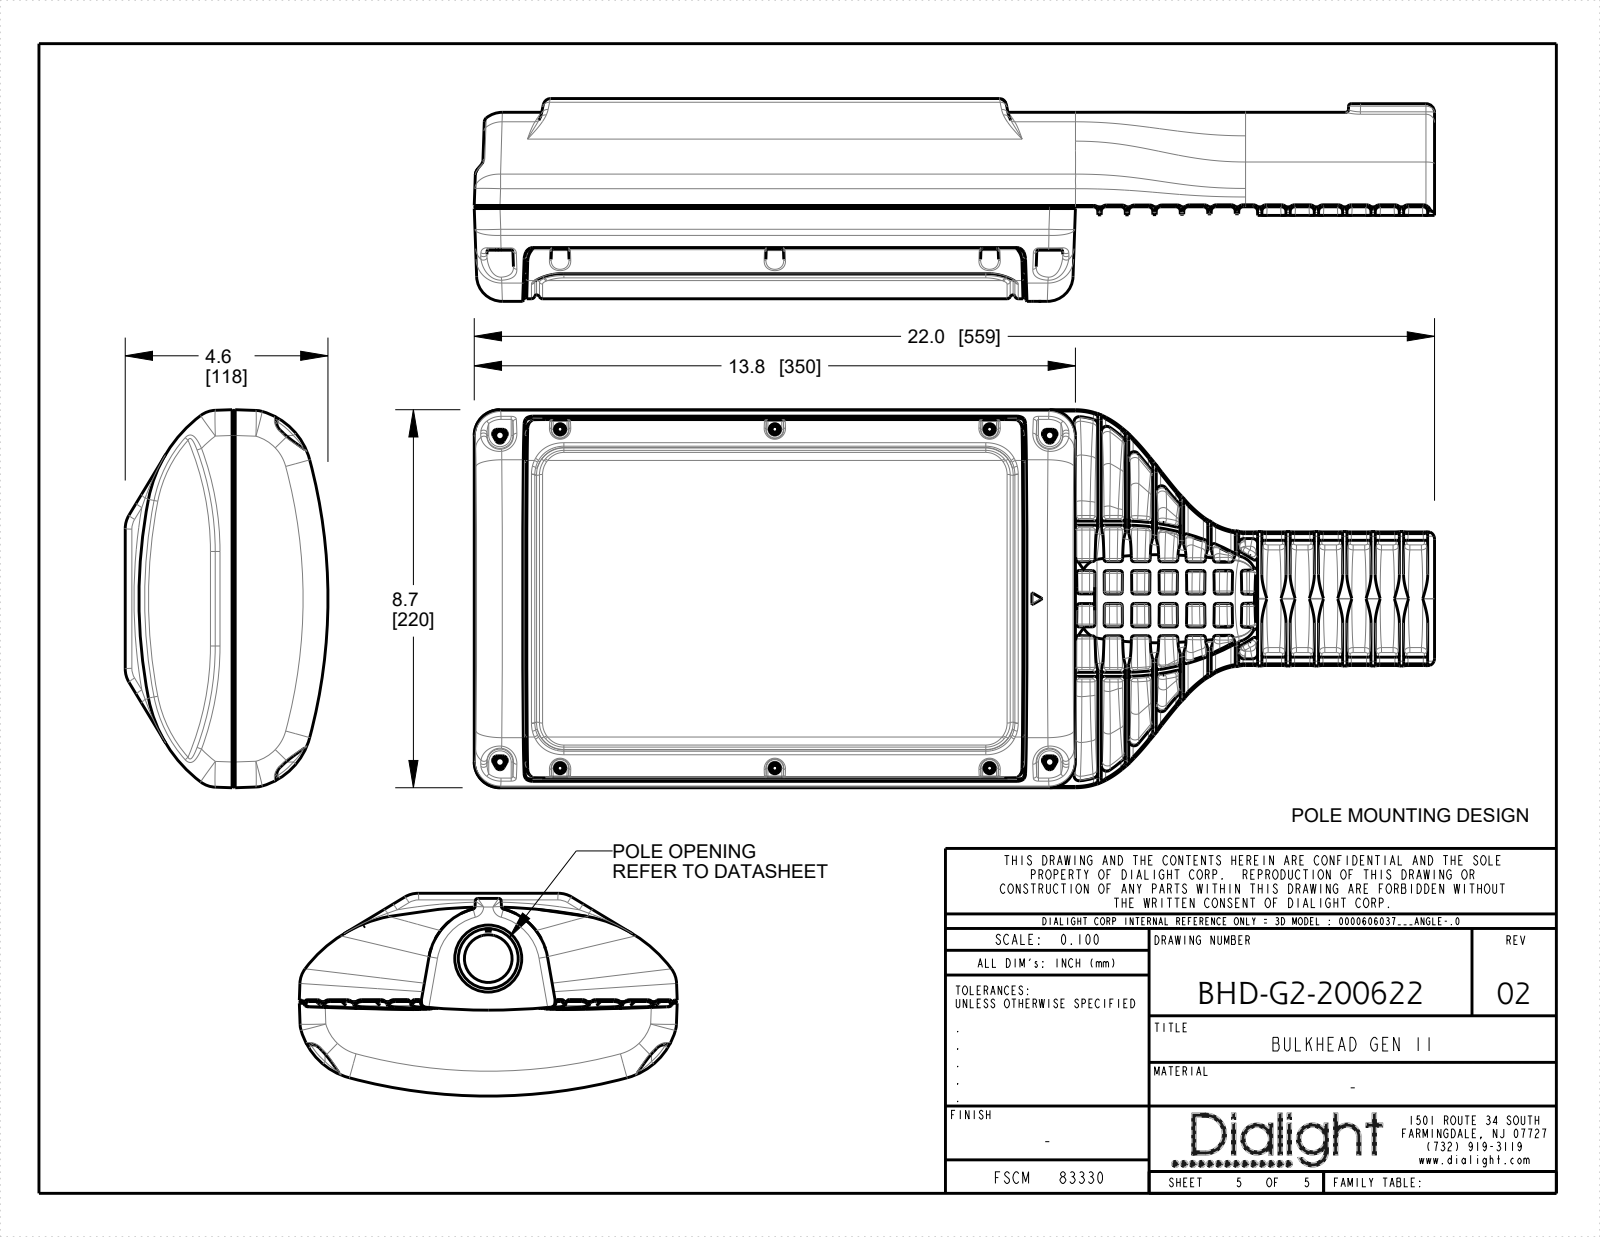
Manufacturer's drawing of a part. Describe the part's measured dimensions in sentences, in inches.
The part is named "001". Its 3-D file was written by "CREO PARAMETRIC BY PTC INC, 2019080 (CONFIG_CONTROL_DESIGN)". It is 0 solids with 380 faces: 67 planar, 93 cylindrical and 220 other. Overall it measures 13.777 by 8.659 by 4.646 inches. Partial cylindrical surfaces (rounded edges, fillets, slot ends): 14 of radius 0.039, 14 of radius 0.079, 14 of radius 0.591, 4 of radius 0.118, 2 of radius 0.394, 2 of radius 0.433, 2 of radius 1.516, 2 of radius 1.575. The main face-to-face distances are 13.603, 8.653, 13.766, 0.163, 12.558, 1.045, 1.208, 8.455, 0.198, 6.171.
